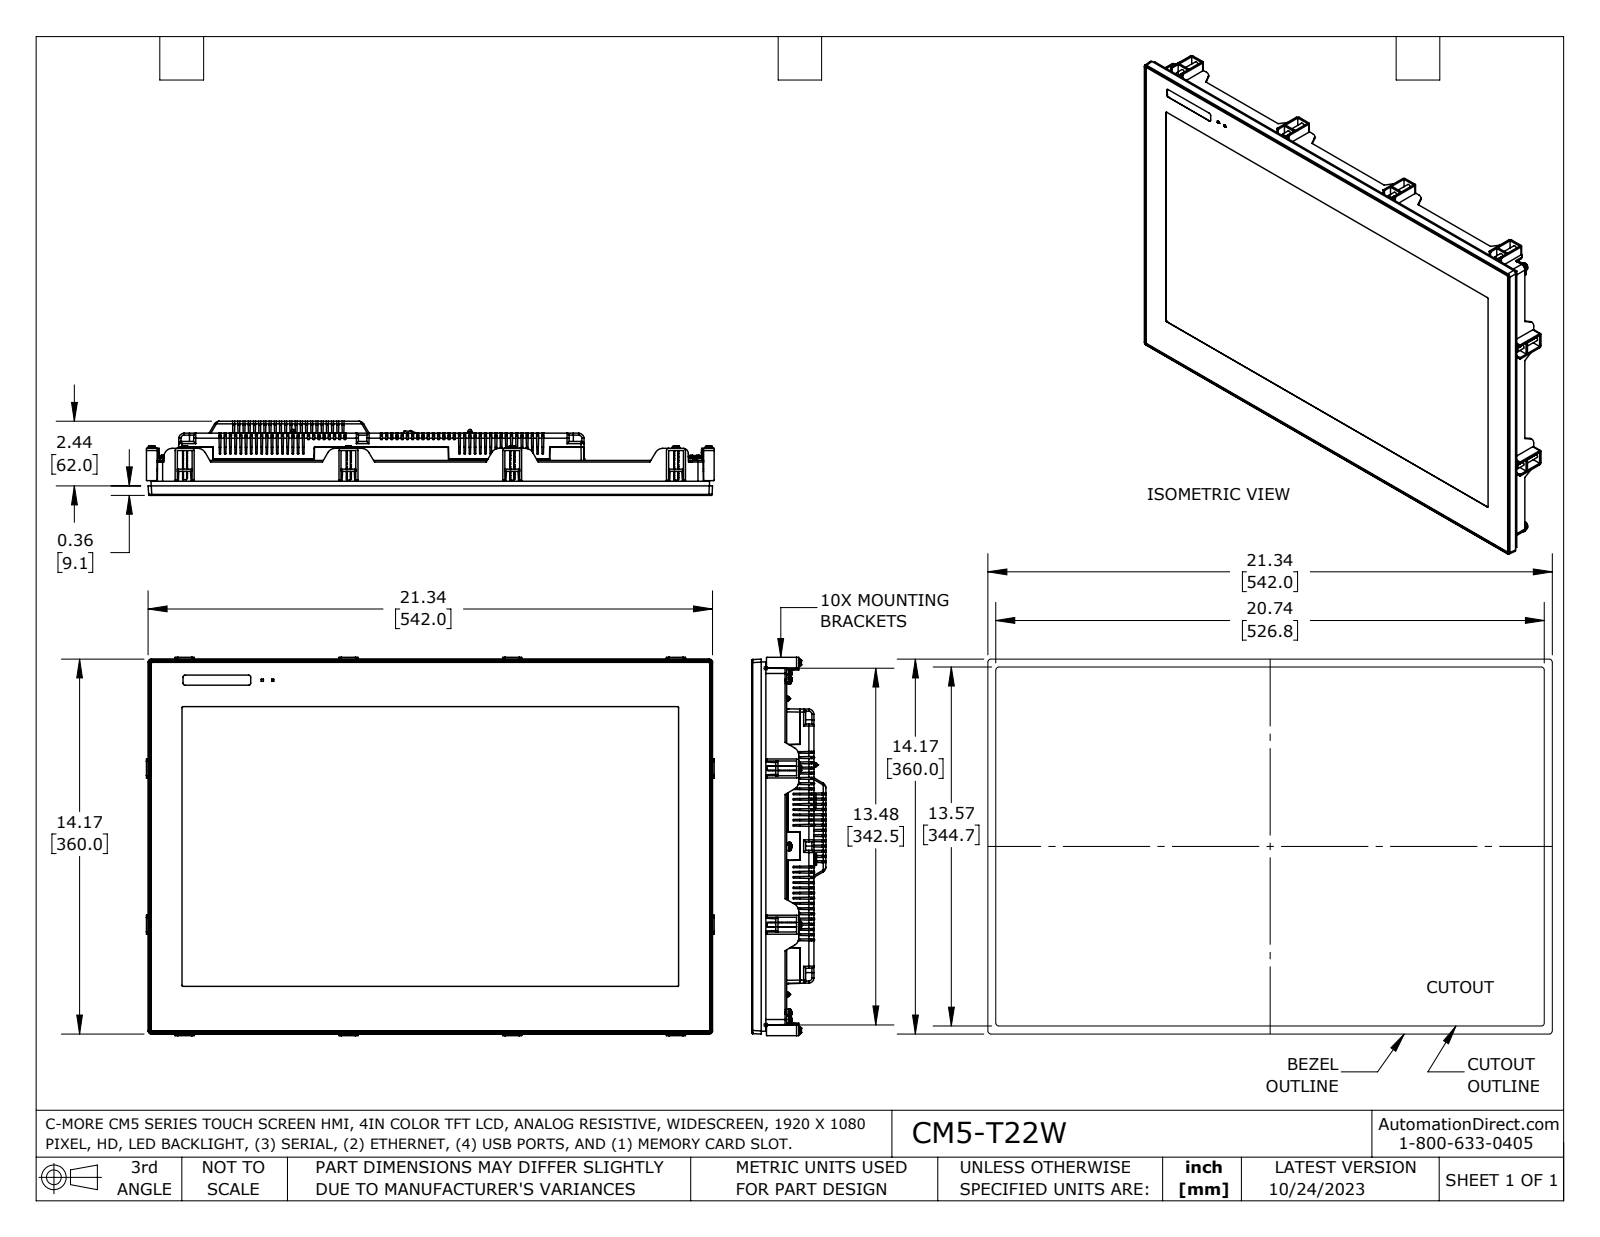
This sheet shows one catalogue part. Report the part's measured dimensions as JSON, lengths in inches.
{"part_name": "CM5-T22W_REV3", "step_written_by": "SolidWorks 2021 (AUTOMOTIVE_DESIGN)", "units": "inches", "bodies": {"solids": 1, "faces": 4563, "planar": 2720, "cylindrical": 1385, "other": 458}, "overall_size": [21.465, 14.299, 2.799], "volume_in3": 529.5, "surface_area_in2": 885.7, "round_holes": [[0.036, 15], [0.161, 10], [0.177, 10], [0.317, 6], [0.11, 4], [0.114, 3], [0.118, 2], [0.201, 1]], "round_bosses_or_shafts": [[0.157, 22], [0.276, 12], [0.327, 10], [0.299, 10], [0.018, 6], [0.102, 4], [0.11, 3], [0.164, 2]], "partial_cylinders_radius": [[0.039, 113], [0.02, 104], [0.079, 75], [0.008, 71], [0.012, 69], [0.038, 24], [0.01, 20], [0.016, 19]], "face_to_face_distances": [1.309, 1.031, 2.341, 2.35, 1.319, 1.48, 0.079, 0.449, 2.789, 2.799], "hole_center_spacings": [0.124, 0.109, 0.218, 0.327, 0.198, 0.294, 0.398, 0.138]}
